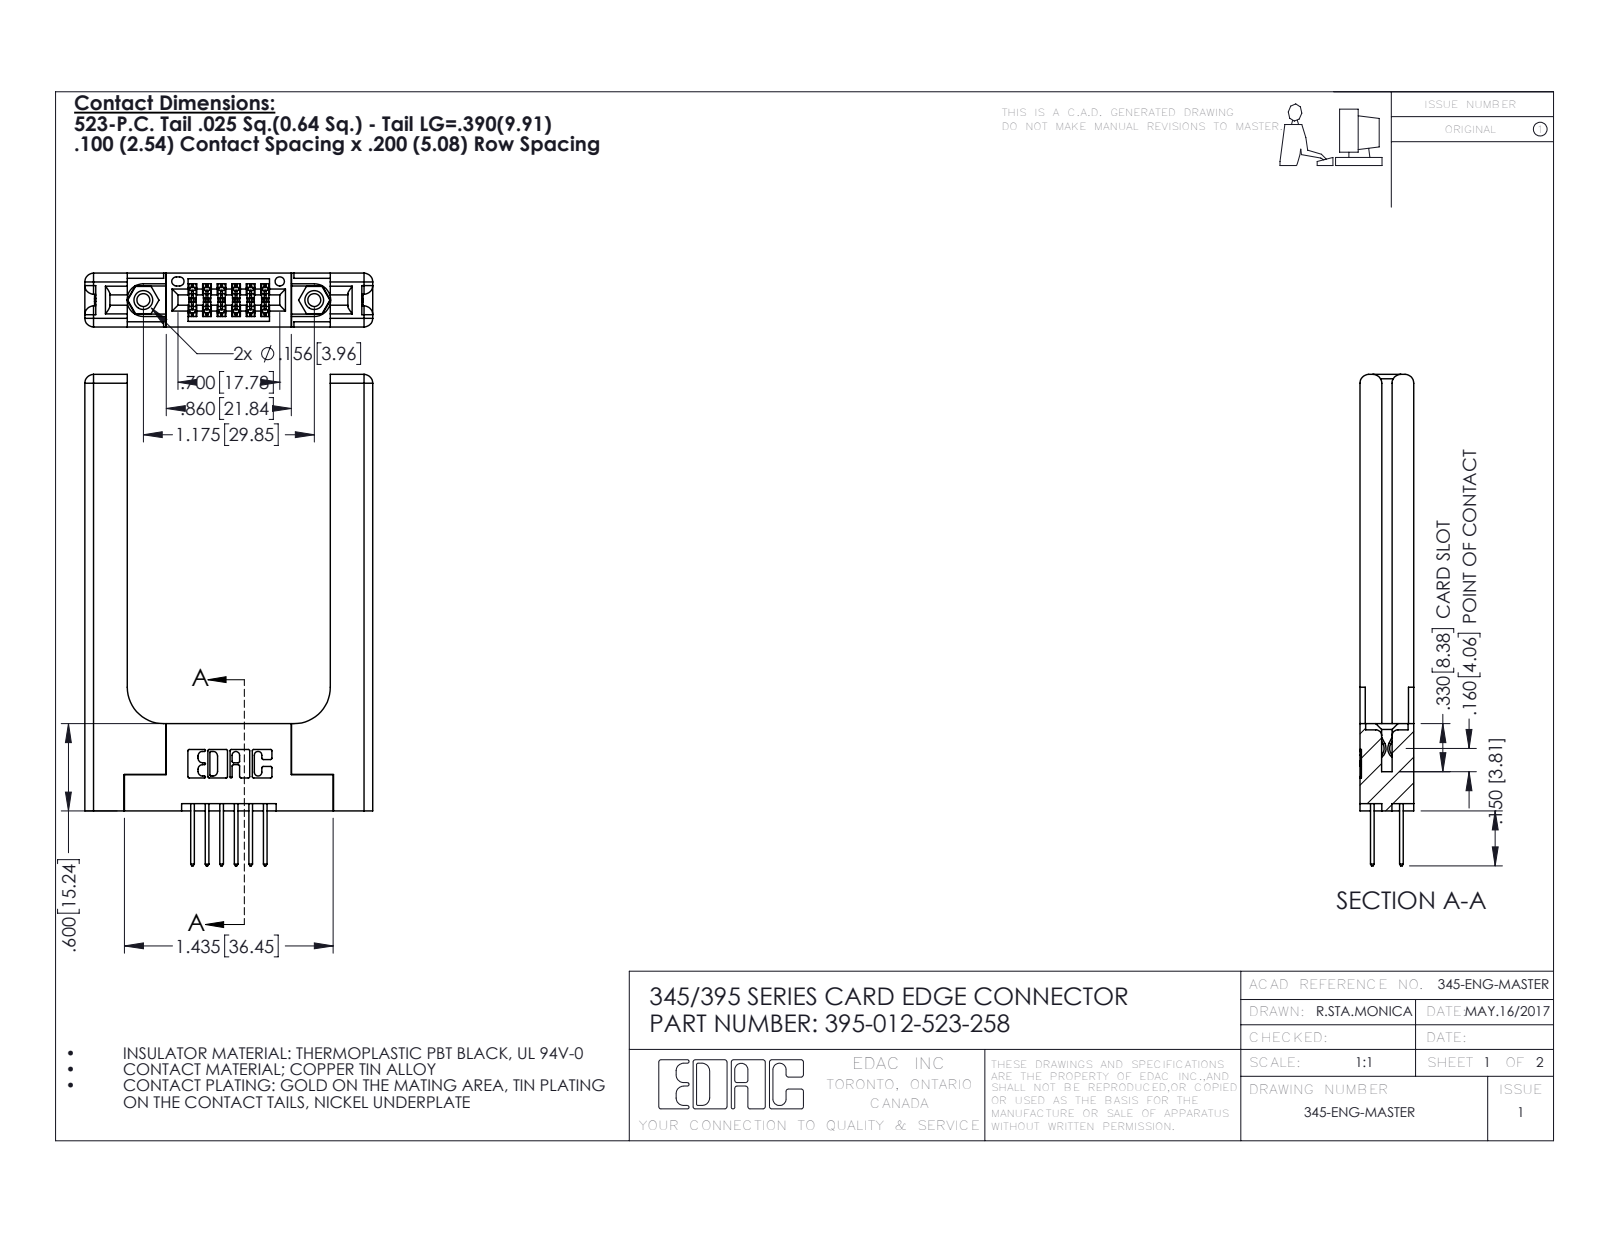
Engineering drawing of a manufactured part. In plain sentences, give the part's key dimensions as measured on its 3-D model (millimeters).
The part is named "345-220-058_345-220-058; 345-250-001_345-250-001-102; 345 Part_Flush Mounting Lugs - 0.156 Dia-TH; 395-012-523-258 (+1 more)". Its 3-D file was written by "SolidWorks 2016 (CONFIG_CONTROL_DESIGN)". It is 17 solids with 982 faces: 624 planar, 298 cylindrical and 60 other. Overall it measures 85.8 by 50.3 by 9.4 millimeters. Its volume is 13 000 cubic millimeters and its surface area 11 230 square millimeters. Round holes: 2 of diameter 2.3, 2 of diameter 3.2, 2 of diameter 4, 1 of diameter 1.6. Round bosses or shafts: 2 of diameter 3.9. Partial cylindrical surfaces (rounded edges, fillets, slot ends): 22 of radius 0.3, 18 of radius 0.2, 16 of radius 1.5, 12 of radius 0.3, 6 of radius 0.2, 6 of radius 0.8, 3 of radius 0.7, 2 of radius 0.4. The main face-to-face distances are 9.4, 3.8, 5.6, 1.8, 2, 3.8, 7.6, 35.5, 5.1, 1.8. The hole center spacings are 6.9, 24, 29.8.
